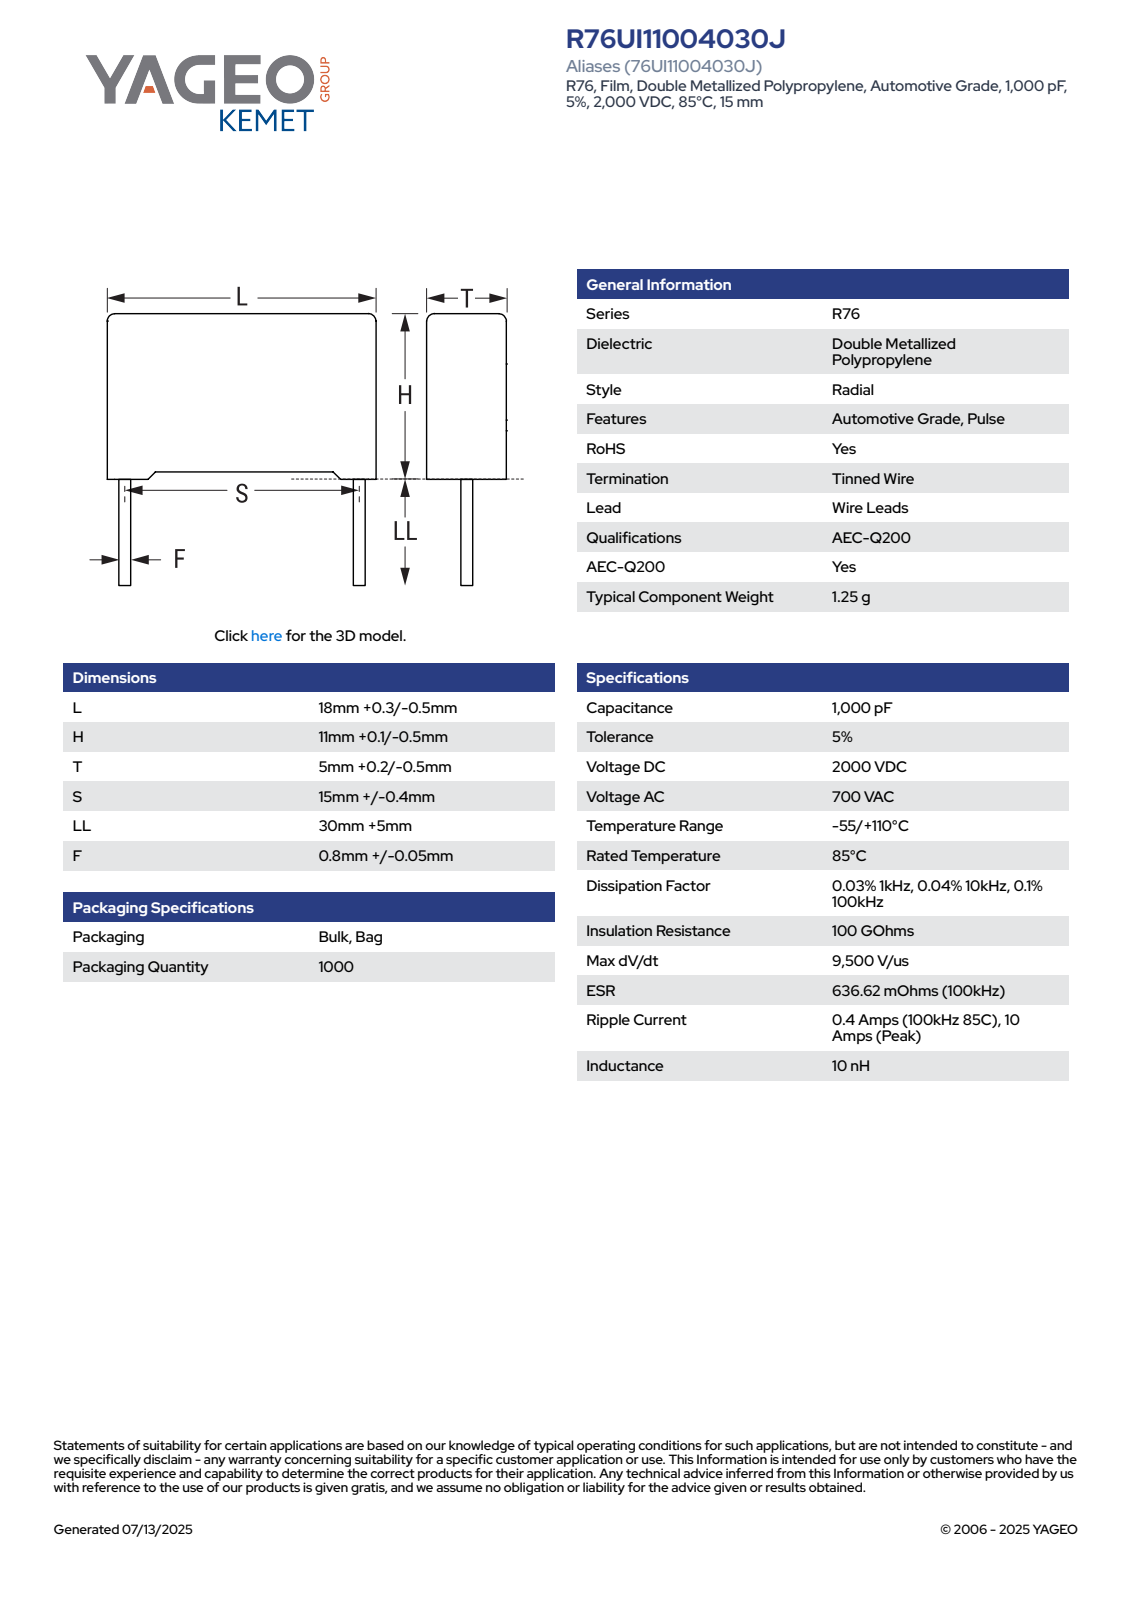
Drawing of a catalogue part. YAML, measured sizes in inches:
part_name: "CFR_RB2_18X11X5_L18.3H11.1T5.2S15LL35F0.85"
step_written_by: "SolidWorks 2021 (AUTOMOTIVE_DESIGN)"
units: inches
bodies: {solids: 4, faces: 85, planar: 77, cylindrical: 8, other: 0}
overall_size: [1.815, 0.72, 0.205]
volume: 0.063
surface_area: 1.44
round_bosses_or_shafts:
  - {diameter: 0.033, count: 2}
partial_cylinders:
  - {radius: 0.02, count: 4}
face_to_face_distances: [0.205, 0.407, 0.72, 0.024, 0.181, 0.015, 0.422, 0.015, 0.03, 0.437]
